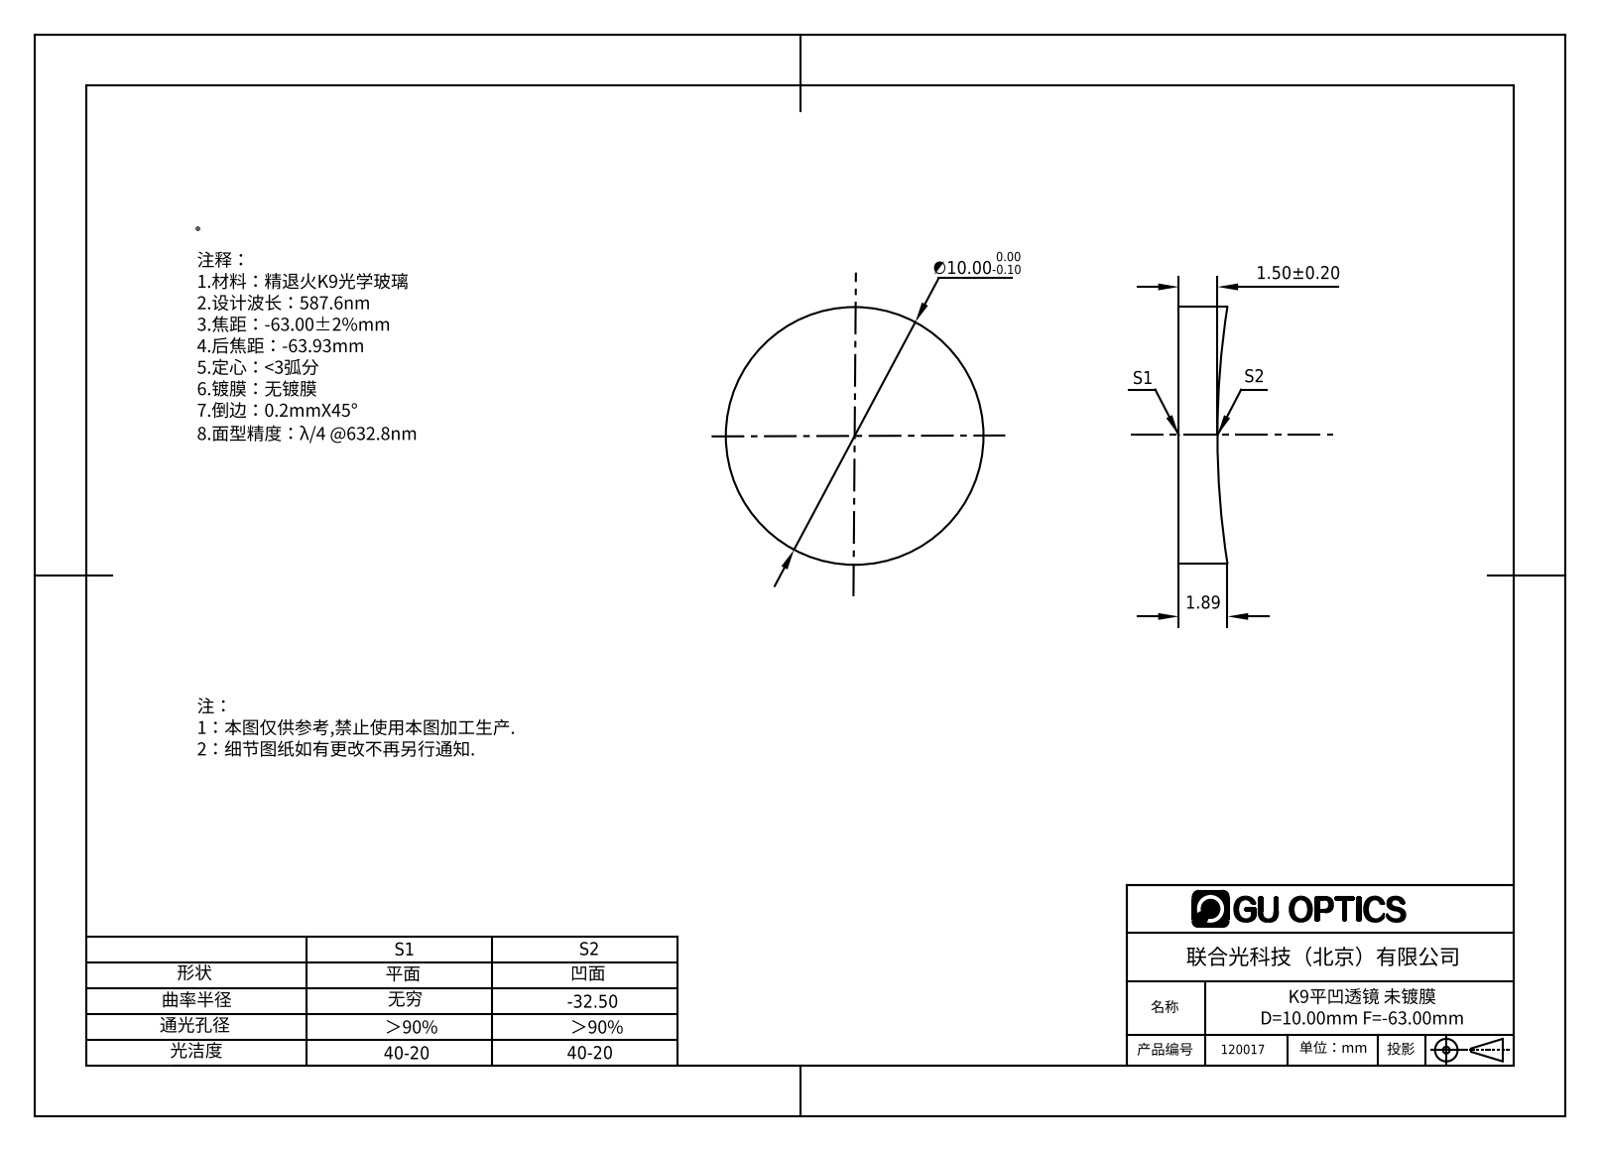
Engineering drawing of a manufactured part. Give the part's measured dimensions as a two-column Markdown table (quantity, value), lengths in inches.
| quantity | value |
| --- | --- |
| part name | 120017 |
| STEP written by | SolidWorks 2016 (AUTOMOTIVE_DESIGN) |
| units | inches |
| bodies | 1 solid, 5 faces (1 planar, 2 cylindrical, 2 other) |
| overall size | 0.394 × 0.394 × 0.074 |
| volume | 0.008 in³ |
| surface area | 0.336 in² |
| round bosses / shafts (diameter × count) | 0.394 × 1 |
